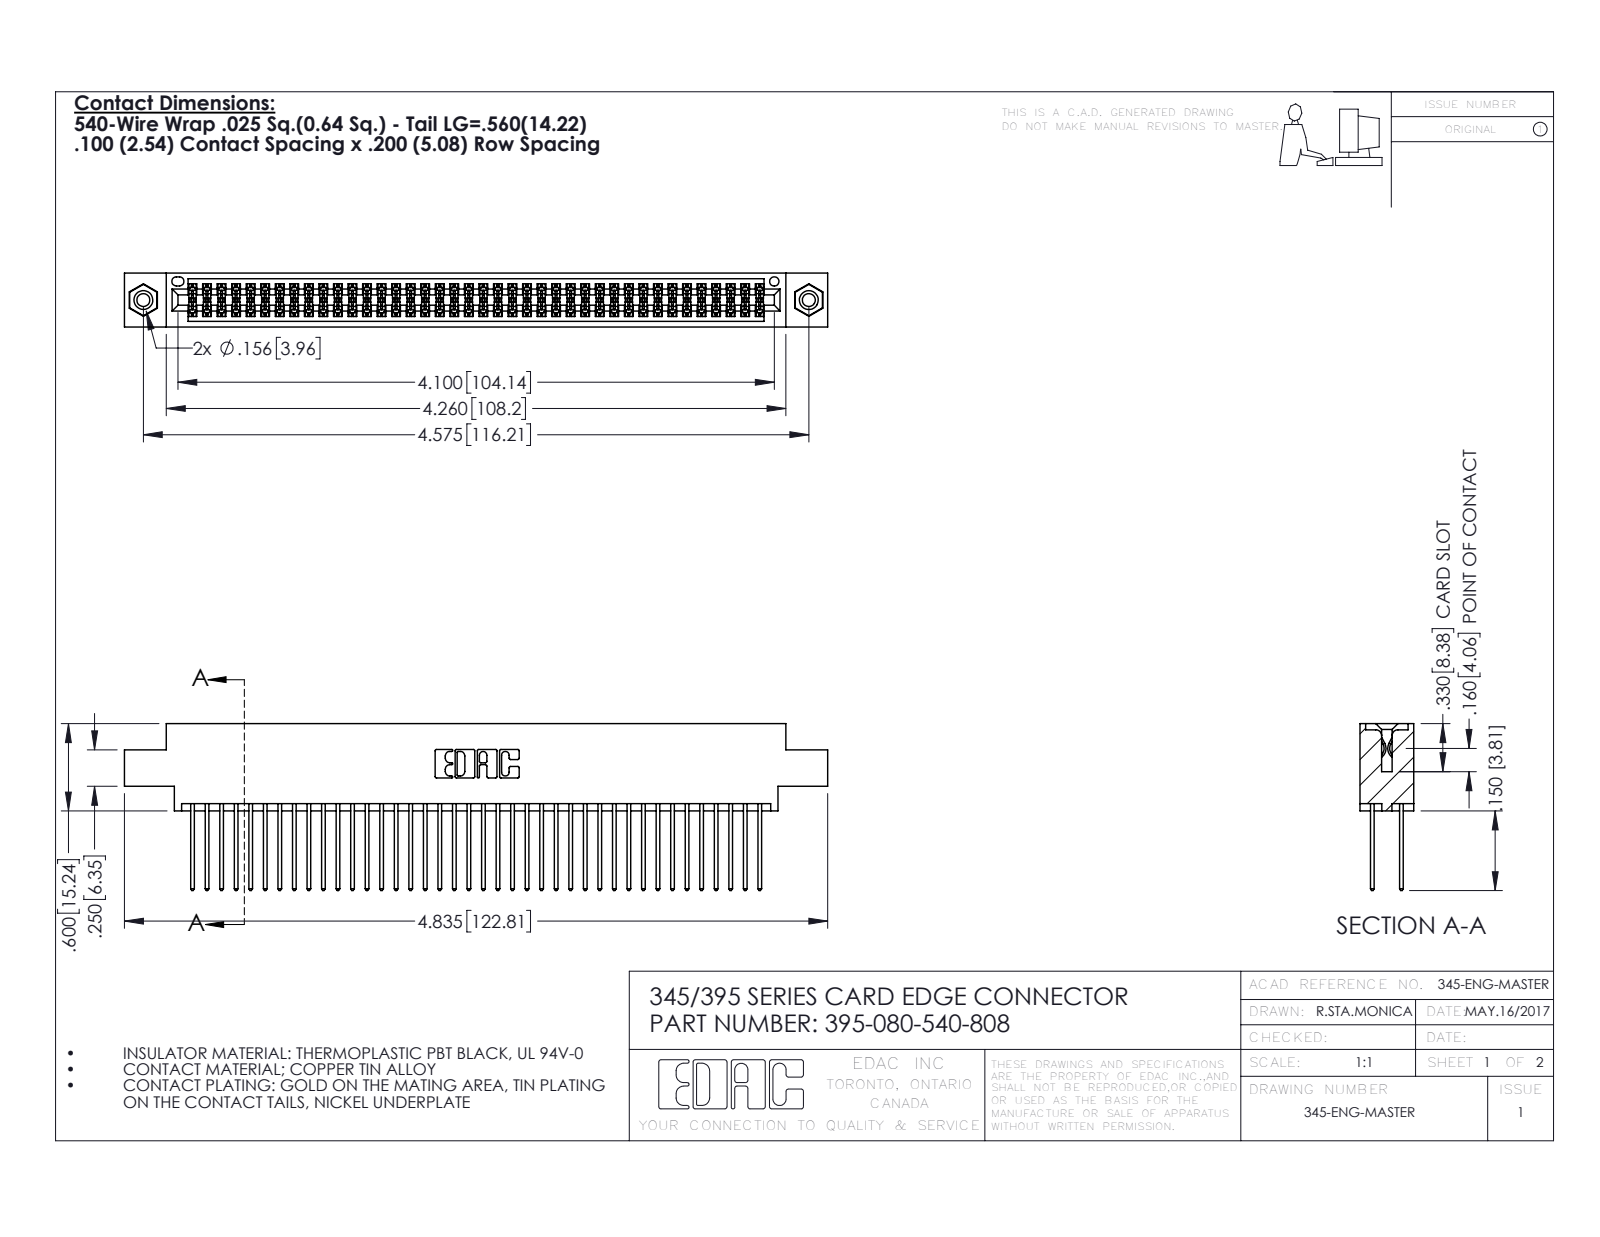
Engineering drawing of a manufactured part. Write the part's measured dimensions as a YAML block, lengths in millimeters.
part_name: "345-292-001_345-293-140; 345 Part_0.170 Offset - 0.156 Dia-TI; 345-250-001_345-250-003-102; 395-080-540-808"
step_written_by: "SolidWorks 2016 (CONFIG_CONTROL_DESIGN)"
units: millimeters
bodies: {solids: 83, faces: 4190, planar: 2756, cylindrical: 1418, other: 16}
overall_size: [122.8, 29.1, 9.4]
volume: 12100
surface_area: 19400
round_holes:
  - {diameter: 2.3, count: 2}
  - {diameter: 3.2, count: 2}
  - {diameter: 4, count: 2}
  - {diameter: 1.6, count: 1}
round_bosses_or_shafts:
  - {diameter: 3.9, count: 2}
partial_cylinders:
  - {radius: 0.2, count: 120}
  - {radius: 0.3, count: 80}
  - {radius: 0.3, count: 22}
  - {radius: 0.2, count: 6}
  - {radius: 0.8, count: 6}
  - {radius: 0.7, count: 3}
  - {radius: 0.4, count: 2}
  - {radius: 0.5, count: 2}
face_to_face_distances: [1.8, 7.6, 5.1, 2.5, 6.9, 0.6, 9.4, 5.7, 4.4, 3.8]
hole_center_spacings: [6.9, 110.2, 116.2]
